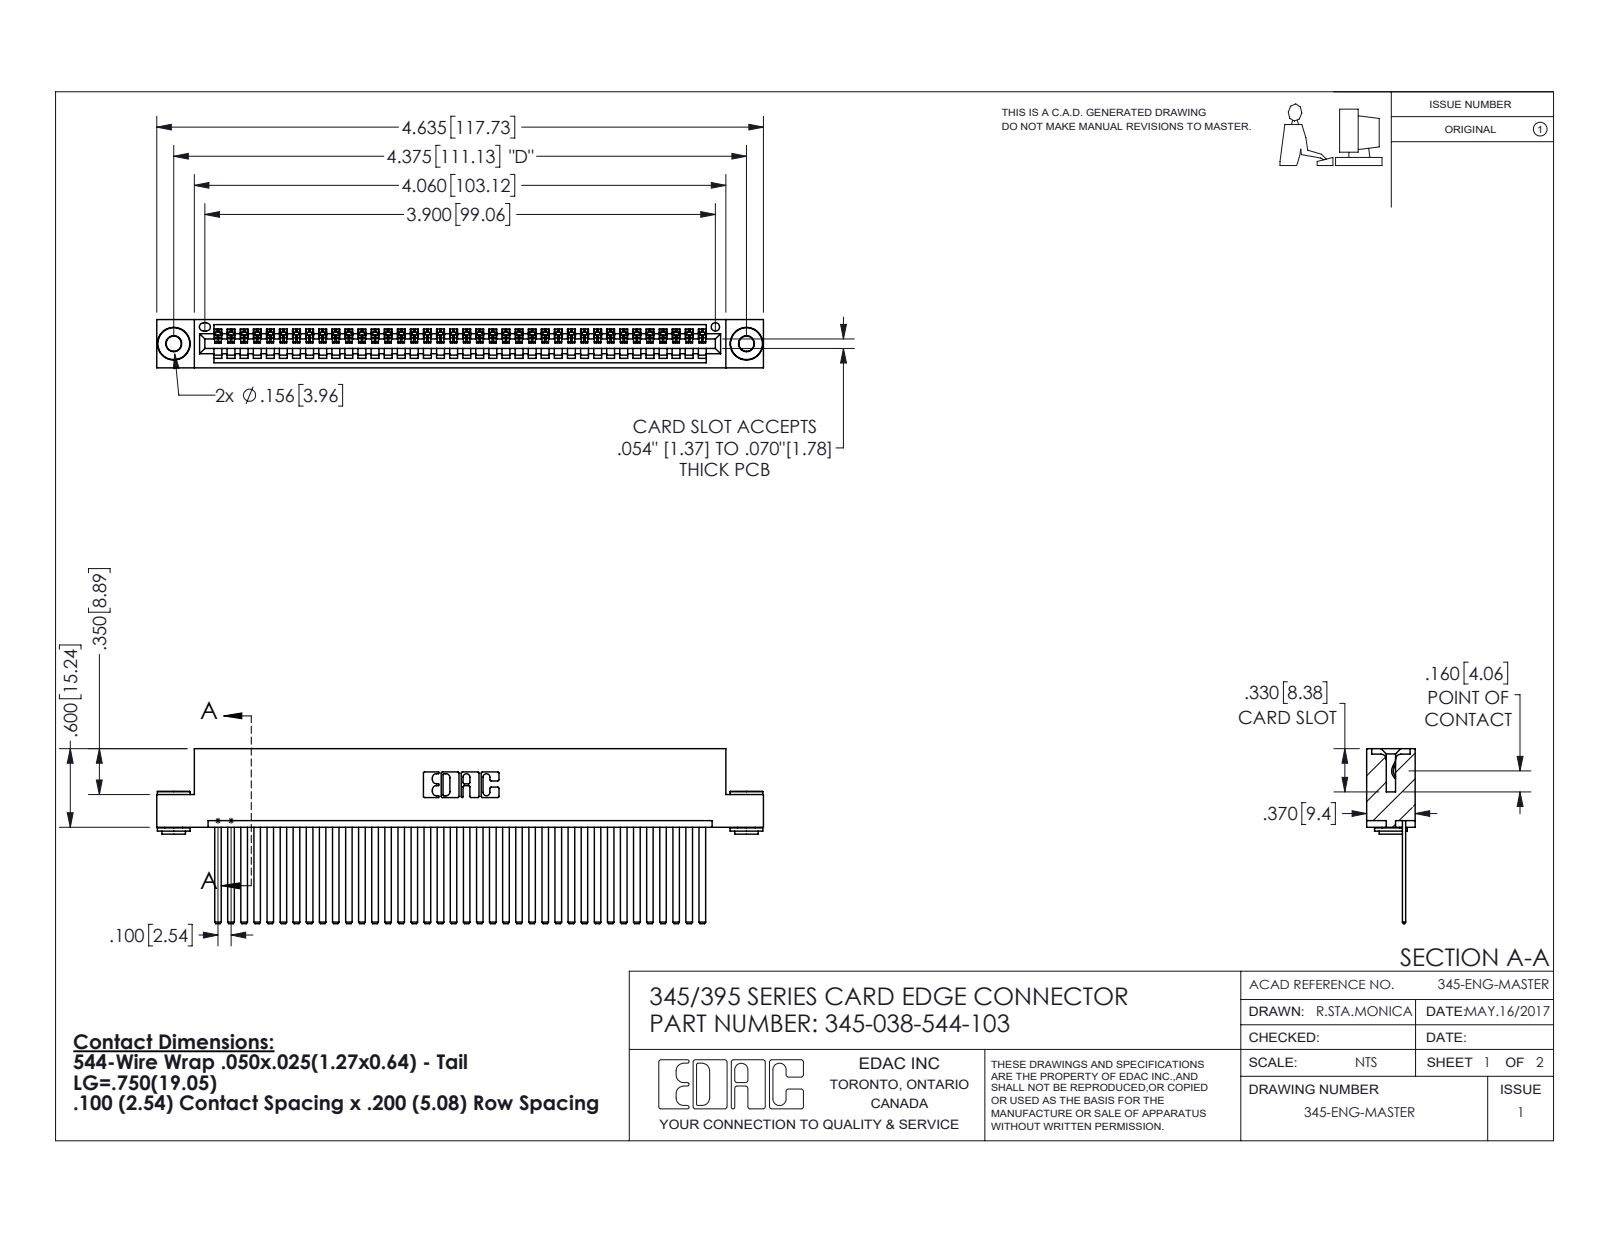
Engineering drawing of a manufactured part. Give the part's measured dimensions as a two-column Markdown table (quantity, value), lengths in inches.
| quantity | value |
| --- | --- |
| part name | 345-038-544-103; 345-250-002_345-250-002-102; 345 Part_Flush Mounting Lugs - 0.156 Dia-TH; 345-292-001_345-293-144 |
| STEP written by | SolidWorks 2016 (CONFIG_CONTROL_DESIGN) |
| units | inches |
| bodies | 41 solids, 2140 faces (1458 planar, 674 cylindrical, 8 other) |
| overall size | 4.635 × 1.337 × 0.37 |
| volume | 0.708 in³ |
| surface area | 26.21 in² |
| round holes (diameter × count) | 0.116 × 2, 0.156 × 2, 0.064 × 1 |
| round bosses / shafts (diameter × count) | 0.25 × 2, 0.18 × 2, 0.136 × 2 |
| partial cylindrical surfaces (radius × count) | 0.006 × 76, 0.01 × 22, 0.007 × 6, 0.031 × 6, 0.026 × 3, 0.031 × 2, 0.04 × 2, 0.014 × 1 |
| main face-to-face distances | 0.072, 0.298, 0.025, 0.098, 0.272, 0.2, 0.37, 0.225, 0.149, 0.072 |
| hole center spacings | 0.27, 4.139, 4.375 |
